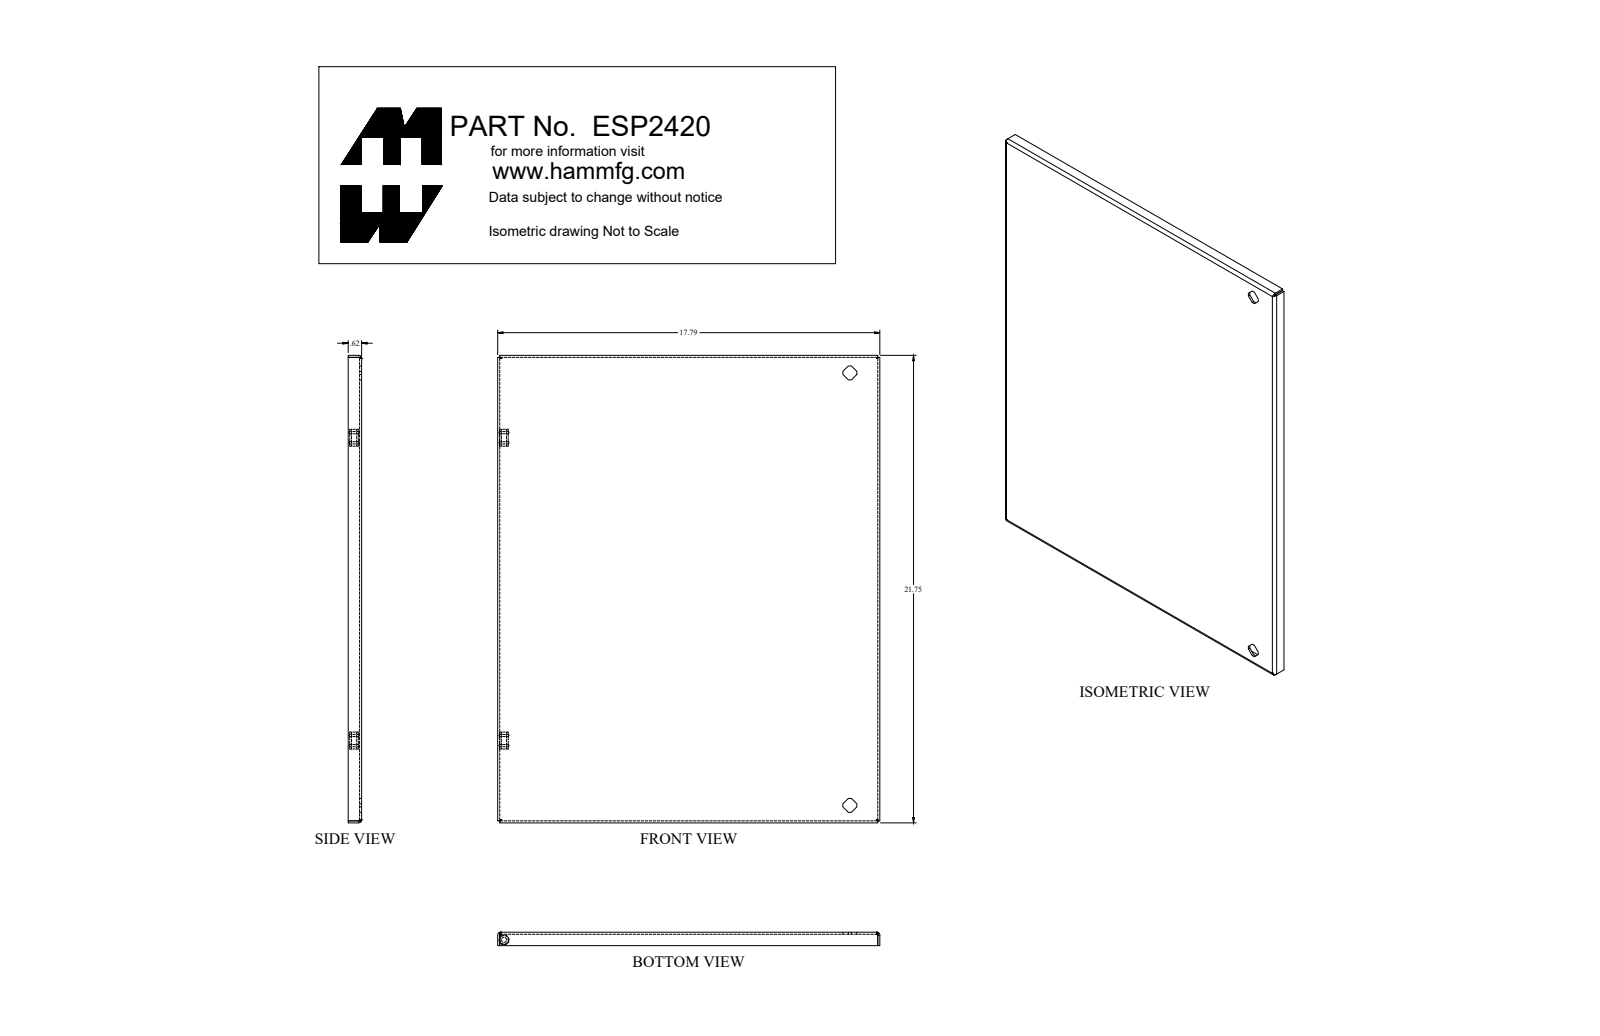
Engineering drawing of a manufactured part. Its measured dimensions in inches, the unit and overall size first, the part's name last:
Units: inches
Overall size (bounding box): 21.75 × 19.886 × 6.246
Round holes (diameter × count): ⌀0.281 ×4, ⌀0.172 ×2, ⌀0.242 ×2, ⌀0.516 ×2, ⌀0.24 ×1
Round bosses / shafts (diameter × count): ⌀0.788 ×2, ⌀0.496 ×2, ⌀0.435 ×2, ⌀0.356 ×2, ⌀0.292 ×2, ⌀0.226 ×2, ⌀0.535 ×1, ⌀0.535 ×1
Partial cylindrical surfaces — rounded edges, fillets, slot ends (radius × count): R0.048 ×28, R0.01 ×24, R0.036 ×6, R0.108 ×6, R0.006 ×4, R0.06 ×4, R0.063 ×4, R0.143 ×4
Main face-to-face distances: 0.095, 0.072, 0.038, 0.775, 0.748, 0.843, 18.26, 0.82, 0.915, 18.188
Hole centre spacings: 4.375, 20, 20.473, 20.159
Volume: 53.77 in³ · Surface area: 1 290 in²
Bodies: 17 solids, 680 faces (378 planar, 230 cylindrical, 72 other)
Part name (STEP PRODUCT): ESP2420
STEP written by: SolidWorks 2018 (AUTOMOTIVE_DESIGN)
